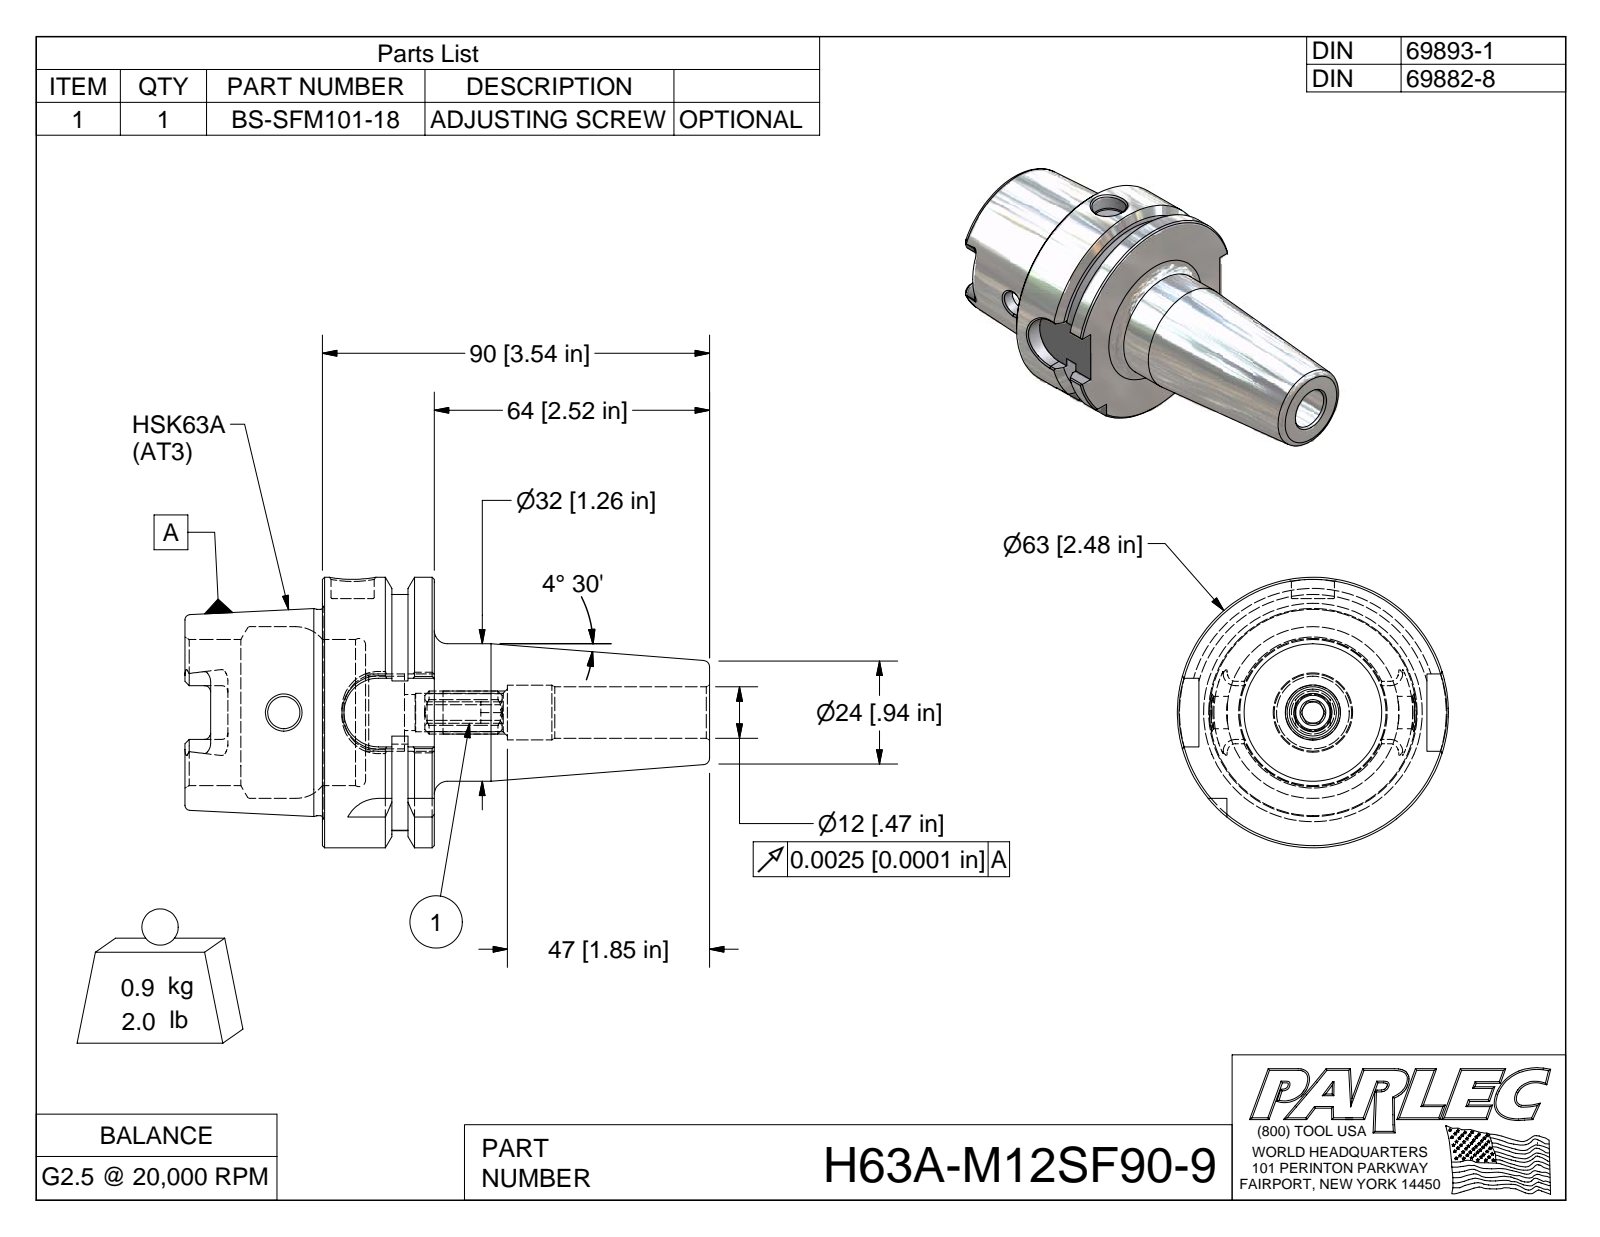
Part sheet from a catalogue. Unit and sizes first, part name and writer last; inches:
Units: inches
Overall size (bounding box): 4.803 × 2.48 × 2.48
Round holes (diameter × count): ⌀0.295 ×1, ⌀0.394 ×1, ⌀0.471 ×1, ⌀0.501 ×1, ⌀0.666 ×1, ⌀1.339 ×1, ⌀1.575 ×1
Round bosses / shafts (diameter × count): ⌀2.48 ×1, ⌀1.891 ×1, ⌀1.26 ×1
Partial cylindrical surfaces — rounded edges, fillets, slot ends (radius × count): R0.059 ×6, R0.113 ×4, R0.315 ×4, R0.197 ×1, R1.083 ×1
Main face-to-face distances: 1.024, 0.241, 0.389, 0.63, 0.394, 1.26, 1.654, 2.283, 0.148, 1.894
Volume: 7.218 in³ · Surface area: 47.67 in²
Bodies: 2 solids, 157 faces (58 planar, 35 cylindrical, 64 other)
Part name (STEP PRODUCT): H63A-M12SF90-9; H63A-M12SF90-9-1; BS-SFM101-18
STEP written by: Autodesk Inventor 2009 (AUTOMOTIVE_DESIGN)
